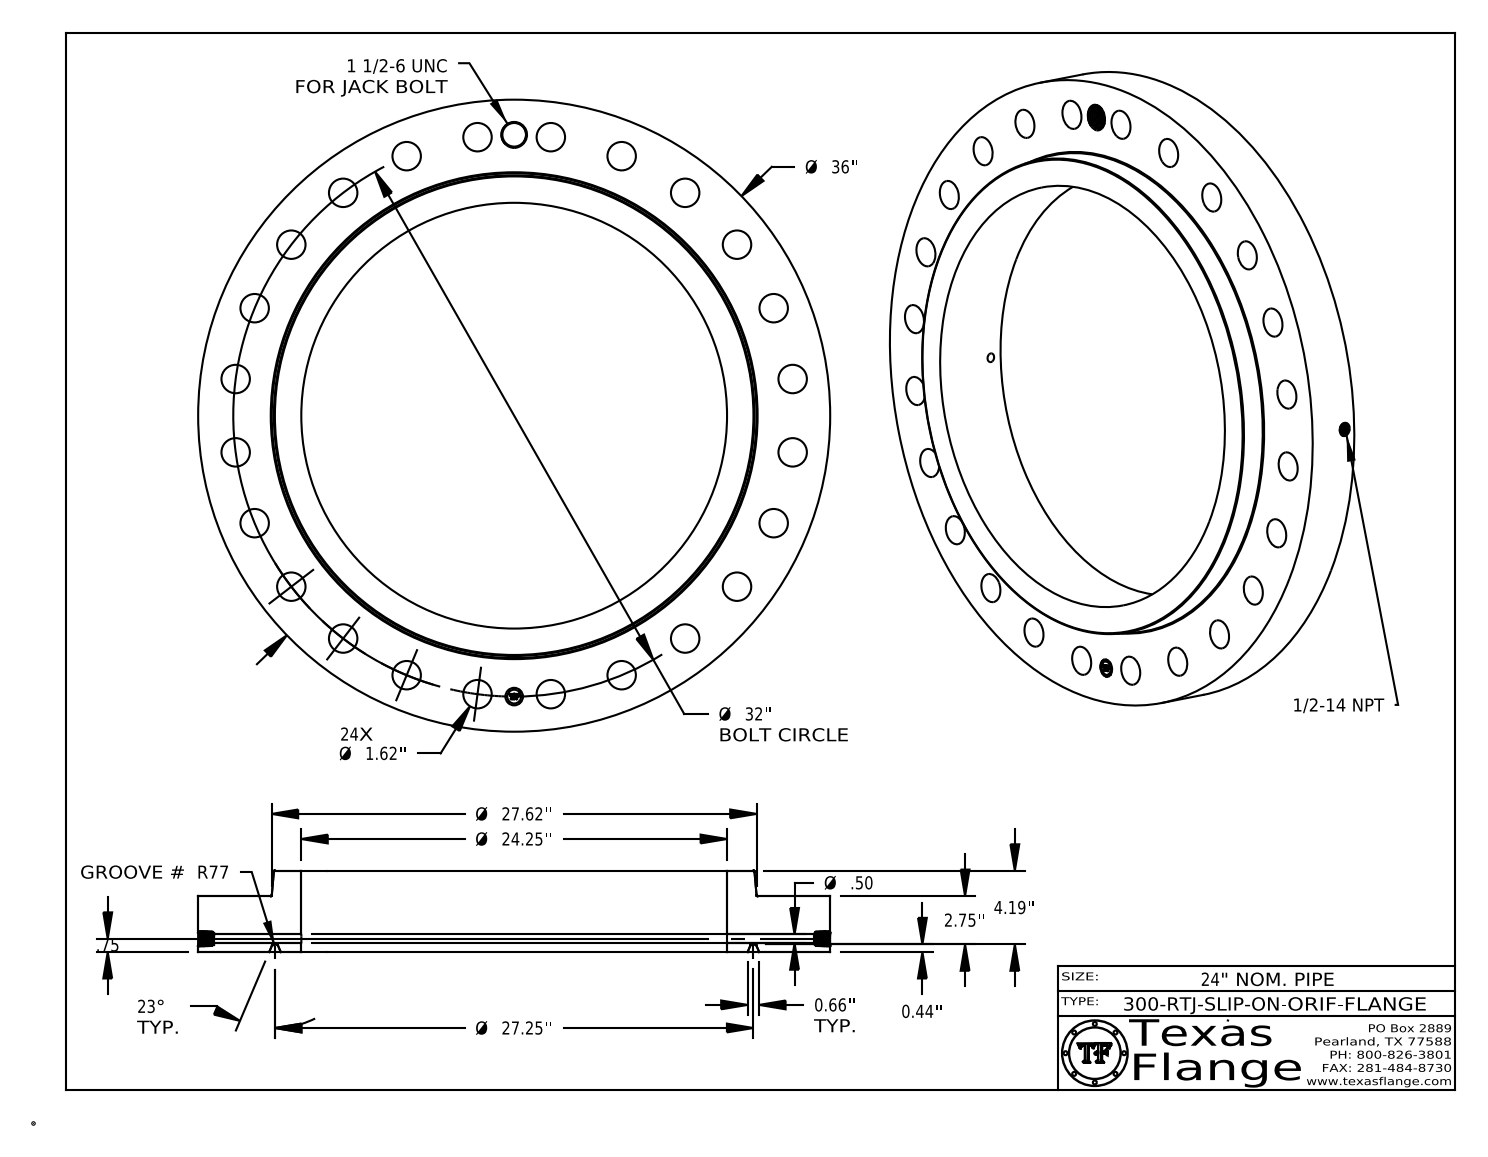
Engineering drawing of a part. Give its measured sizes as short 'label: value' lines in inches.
name: 300-RTJ-SLIP-ON
written by: CATIA V5 STEP AP214 (AUTOMOTIVE_DESIGN)
unit: in
bodies: 1 solid, 831 faces (370 planar, 130 cylindrical, 331 other)
size: 36 × 36 × 4.628
volume: 1 779 in³; area: 2 312 in²
holes: 24× ⌀1.62, 1× ⌀0.5, 1× ⌀0.672, 1× ⌀1, 1× ⌀1.344, 1× ⌀24.25
bosses: 8× ⌀0.061, 1× ⌀36, 1× ⌀0.788
face distances: 3.188, 4.628, 1.44, 0.438, 2.75, 4.19, 0.015, 3.173, 2.735, 1.455
hole spacings: 16, 27.713, 30.909, 4.177, 19.48, 31.726, 8.282, 12.246
